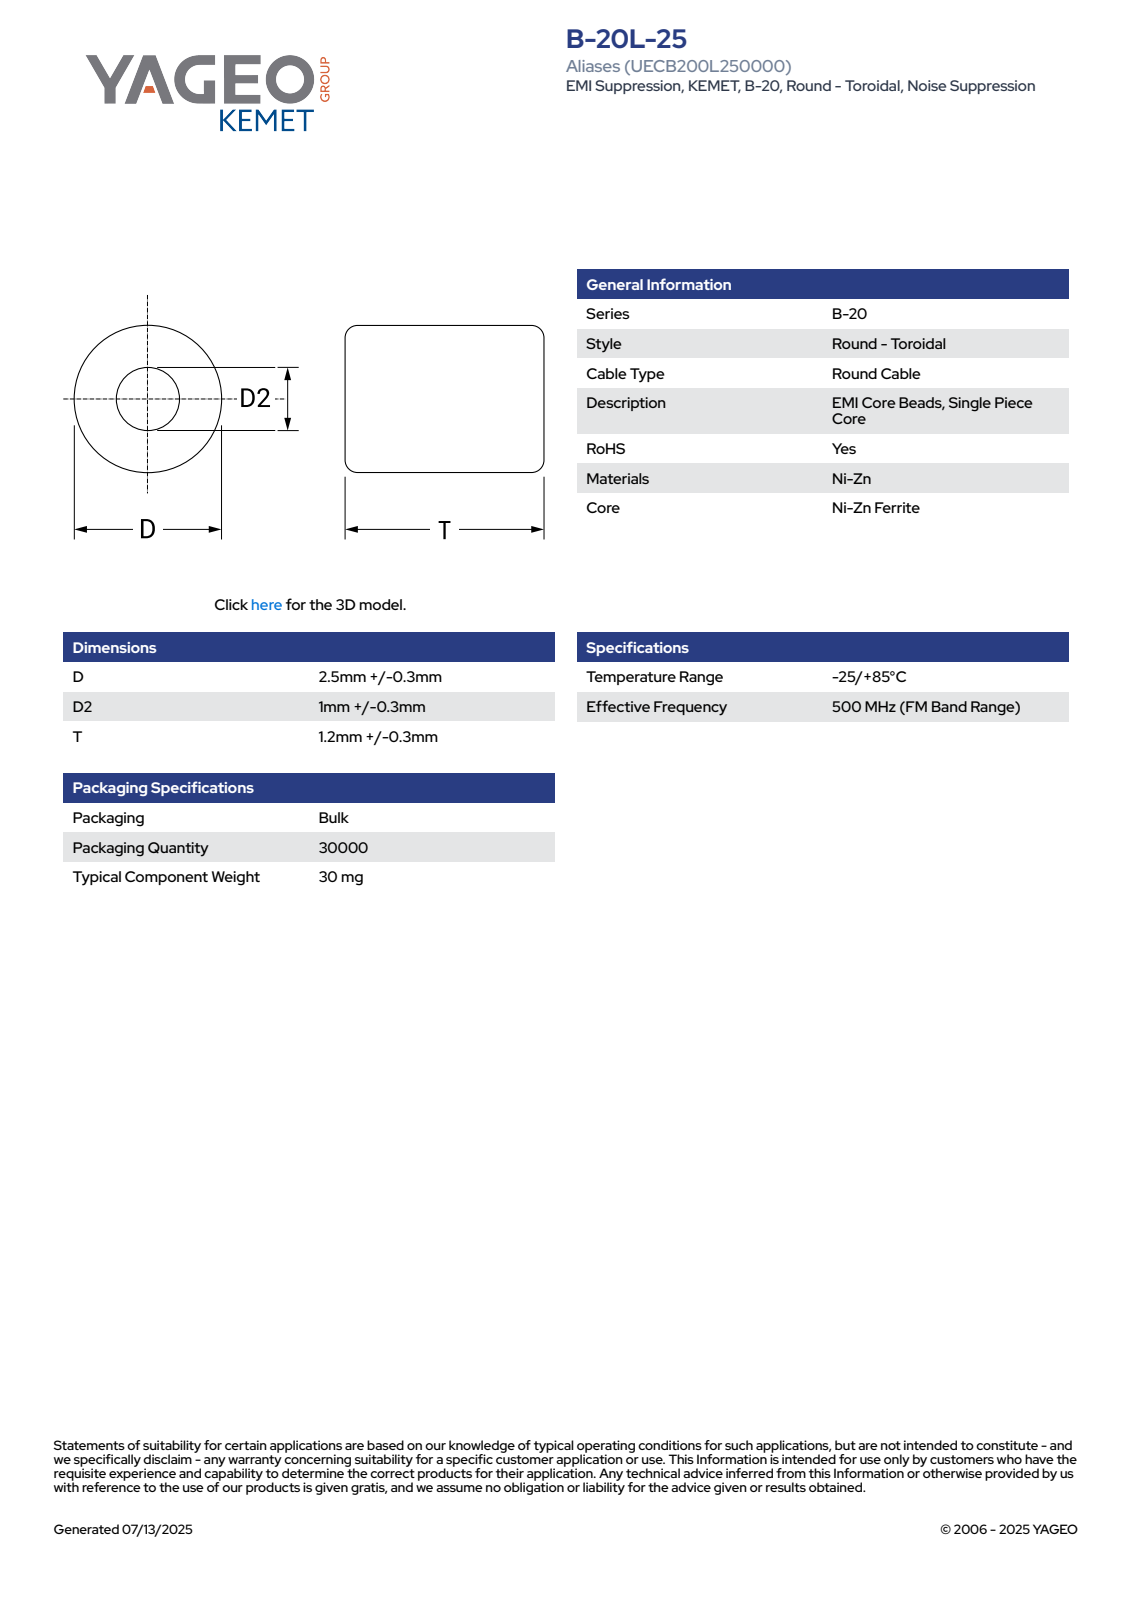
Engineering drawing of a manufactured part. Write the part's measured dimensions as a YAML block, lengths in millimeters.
part_name: "EC_KBCH_D2.8D21T1.5"
step_written_by: "SolidWorks 2021 (AUTOMOTIVE_DESIGN)"
units: millimeters
bodies: {solids: 1, faces: 66, planar: 25, cylindrical: 7, other: 34}
overall_size: [2.81, 2.8, 1.5]
volume: 8
surface_area: 28
round_holes:
  - {diameter: 1, count: 1}
round_bosses_or_shafts:
  - {diameter: 2.8, count: 1}
partial_cylinders:
  - {radius: 1.41, count: 1}
face_to_face_distances: [1.5, 0.56, 0.94, 0.38, 0.63, 0.87, 0.31, 0.8, 0.7, 0.73]
